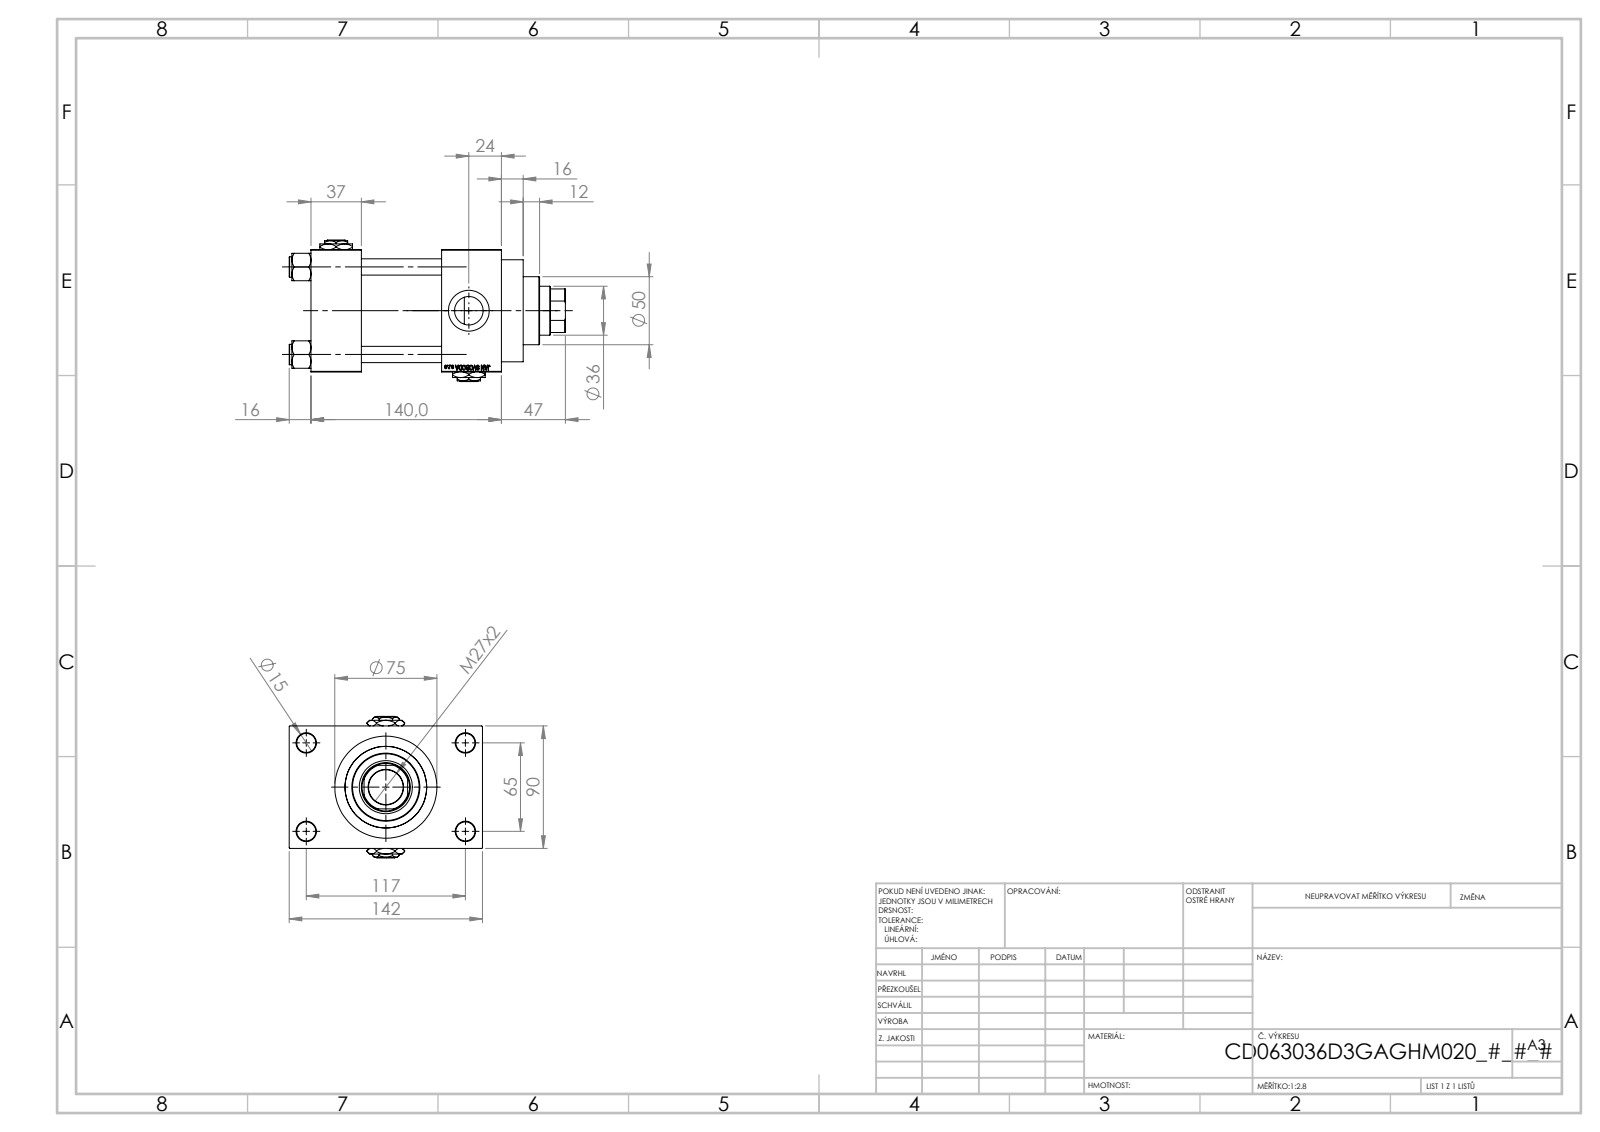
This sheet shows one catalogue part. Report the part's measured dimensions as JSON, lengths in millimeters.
{"part_name": "V215CD_VCP_D; V215CD_NUT_M5_D; V215CD_D_Body; V215CD_D_TYCINKA (+2 more)", "step_written_by": "SolidWorks 2019 (CONFIG_CONTROL_DESIGN)", "units": "millimeters", "bodies": {"solids": 13, "faces": 1194, "planar": 543, "cylindrical": 93, "other": 558}, "overall_size": [203, 142, 104], "volume_mm3": 1111000, "surface_area_mm2": 209110, "round_holes": [[12, 4], [14, 4], [20.96, 3], [30, 3], [7, 2], [25.5, 1], [36, 1], [39, 1], [50, 1], [60, 1], [63, 1]], "round_bosses_or_shafts": [[15, 4], [75, 1], [69, 1]], "partial_cylinders_radius": [[17.5, 1]], "face_to_face_distances": [90, 59, 37, 96, 103, 140, 44, 26, 116, 142], "hole_center_spacings": [26.35, 45.47, 64.3, 66.92, 69.81, 90.65, 111.34, 65]}
